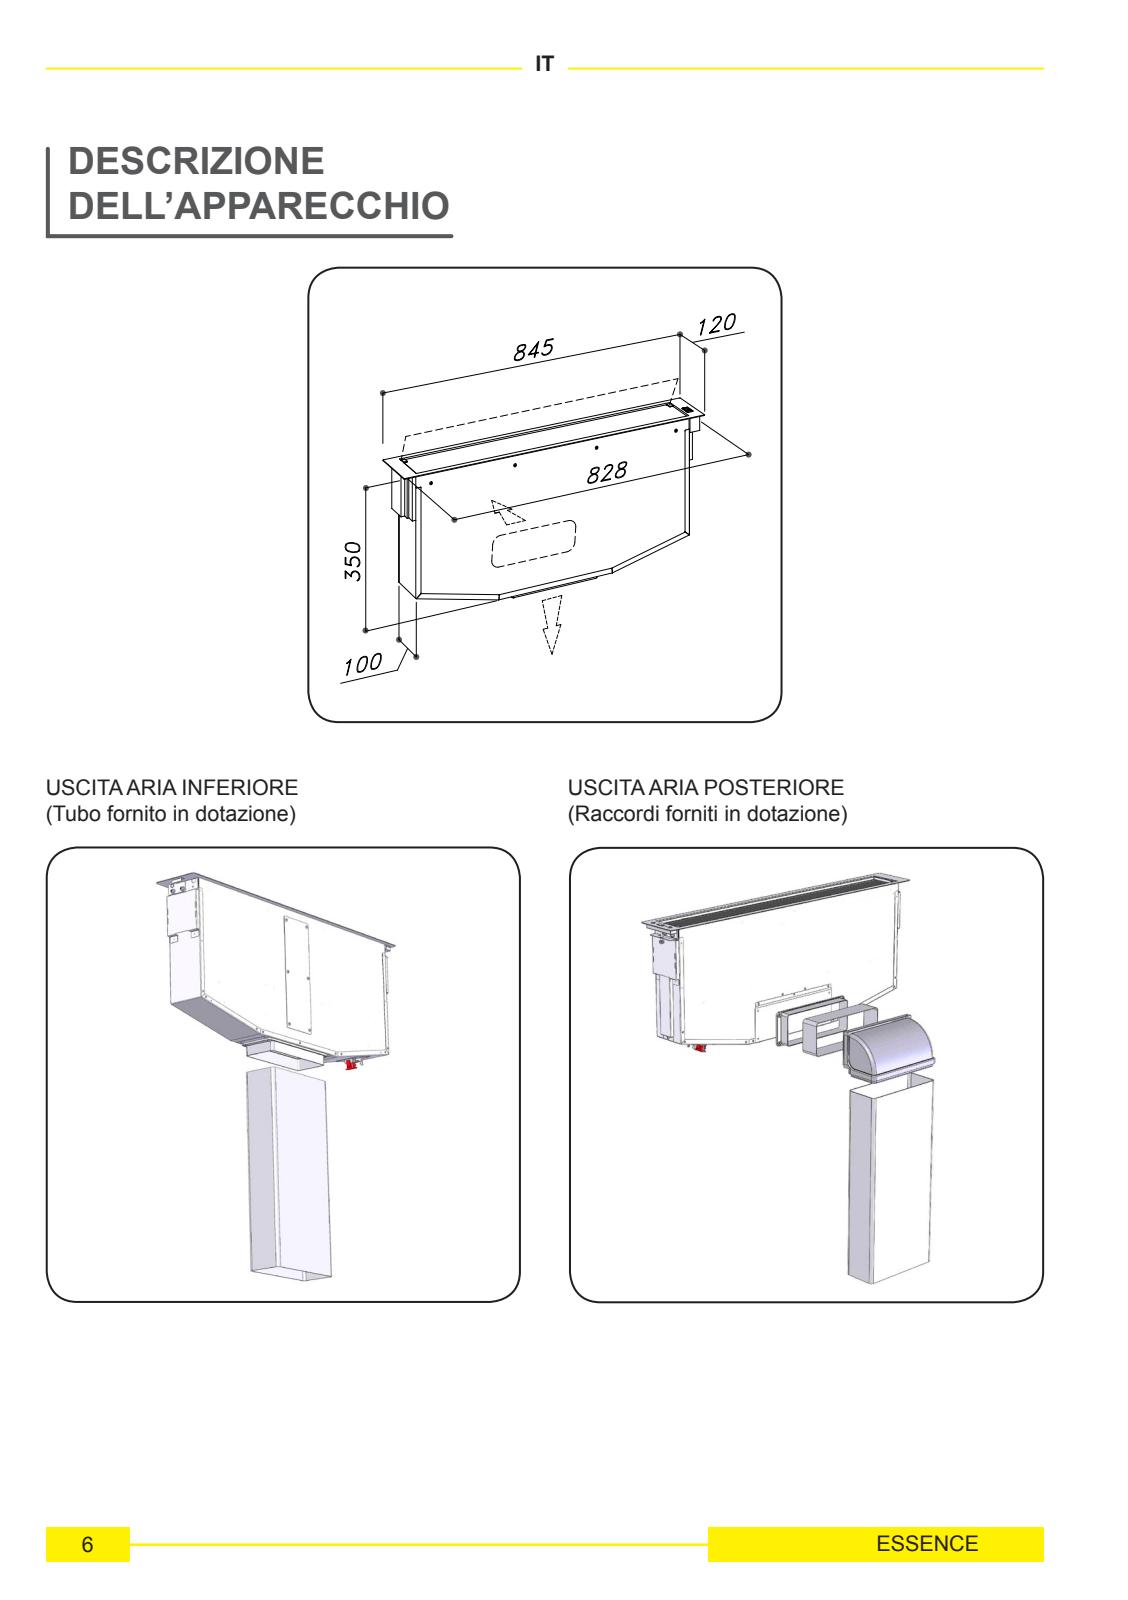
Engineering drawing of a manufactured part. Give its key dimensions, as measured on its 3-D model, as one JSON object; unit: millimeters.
{"part_name": "Sdd16_2016-03-14 PARTE", "step_written_by": "SolidWorks 2016 (AUTOMOTIVE_DESIGN)", "units": "millimeters", "bodies": {"solids": 153, "faces": 9134, "planar": 3289, "cylindrical": 3114, "other": 2731}, "overall_size": [902.3, 845, 138.1], "volume_mm3": 2871000, "surface_area_mm2": 2792000, "round_holes": [[3.5, 56], [2.5, 55], [4, 35], [1.8, 14], [3.2, 8], [3.56, 6], [3.56, 6], [3.8, 6], [4.7, 6], [5.59, 6], [2.2, 4], [3.4, 4]], "round_bosses_or_shafts": [[4.5, 48], [1.8, 48], [2.6, 33], [14.4, 4], [12, 4], [10.4, 4], [7, 4], [5.5, 4]], "partial_cylinders_radius": [[0.2, 606], [2, 144], [0.5, 132], [0.6, 92], [1, 90], [1.4, 32], [1.6, 28], [2.2, 28]], "face_to_face_distances": [0.8, 93.4, 1, 94.2, 92.6, 1.6, 1.8, 0.6, 9.5, 94.4], "hole_center_spacings": [6.35, 8.98, 4.49, 12.7, 14.2, 762, 60, 4.48]}
